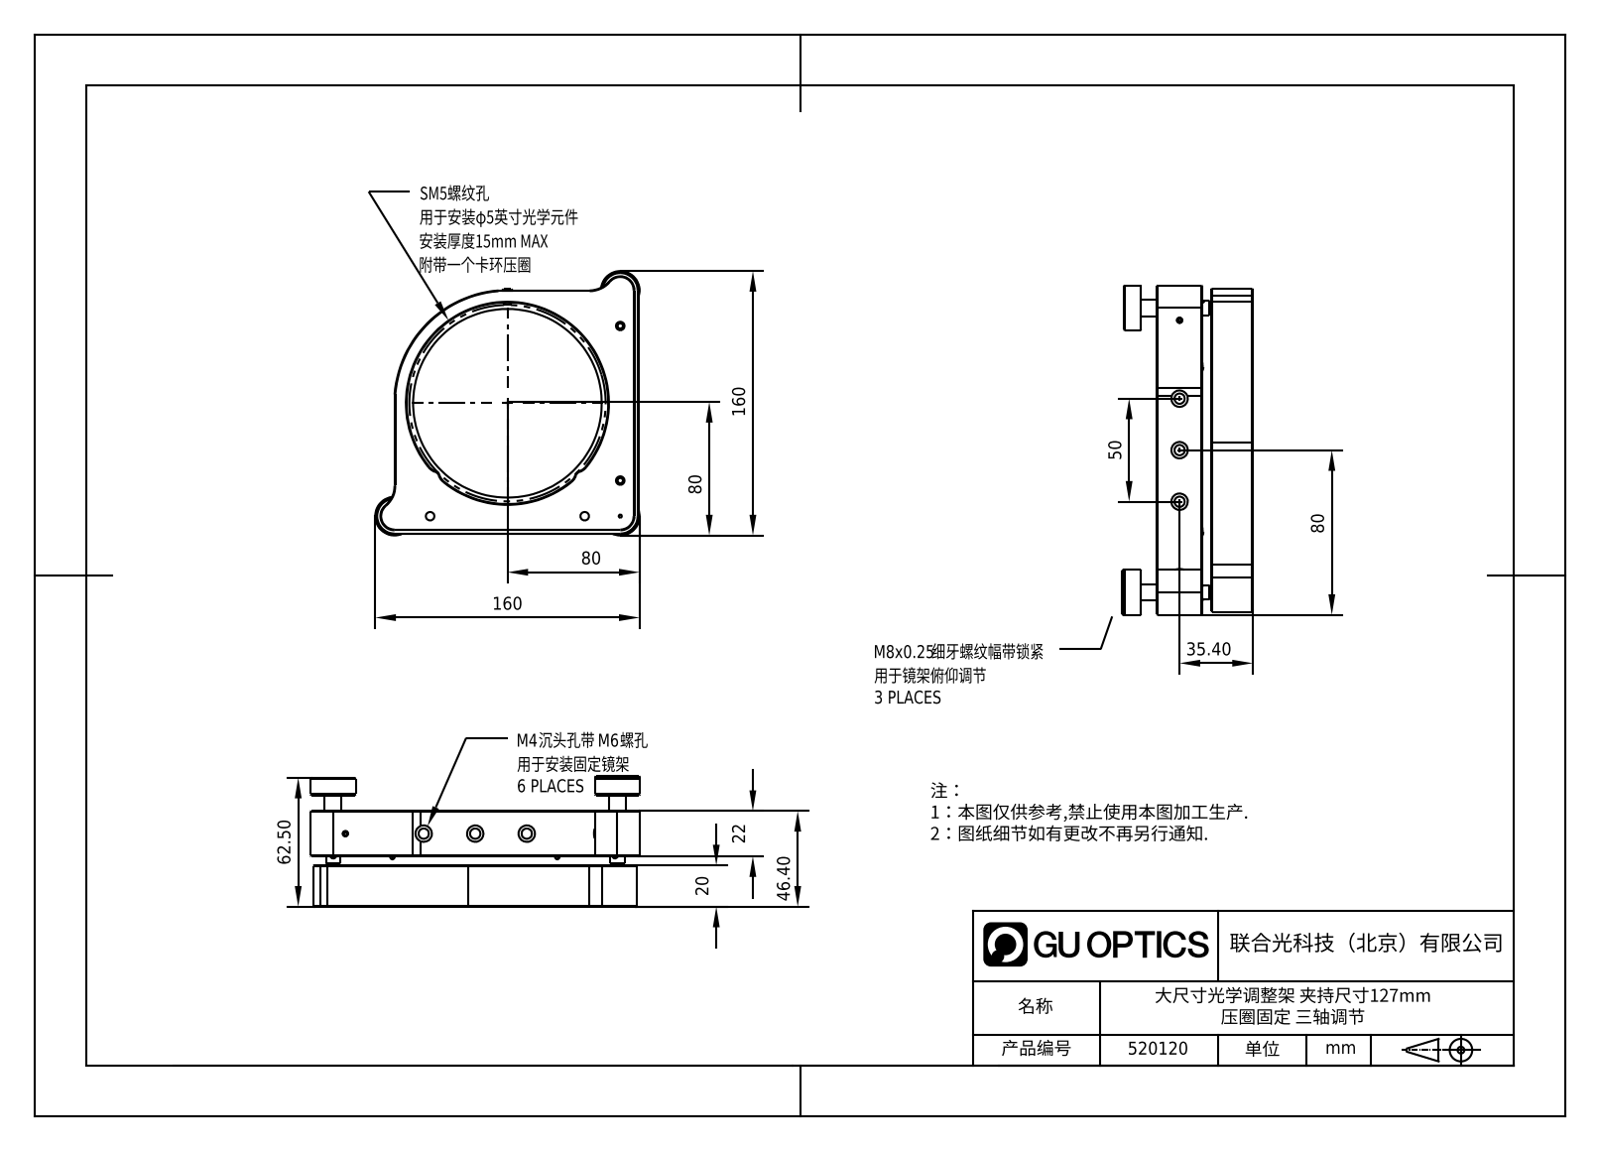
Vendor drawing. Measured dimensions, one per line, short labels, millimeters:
written by: SolidWorks 2021 (CONFIG_CONTROL_DESIGN)
unit: mm
bodies: 0 solids, 352 faces (107 planar, 142 cylindrical, 103 other)
size: 160 × 160 × 63.24
holes: 10× ⌀8, 6× ⌀5, 4× ⌀3.3, 3× ⌀3, 3× ⌀6, 3× ⌀12, 2× ⌀1.5, 2× ⌀2.5, 1× ⌀13.5, 1× ⌀122, 1× ⌀123, 1× ⌀127
bosses: 4× ⌀2, 3× ⌀22, 3× ⌀8, 3× ⌀7, 2× ⌀13
rounds: 8× R1.05, 4× R6, 3× R9.5, 2× R8, 2× R10, 1× R64.5, 1× R72
face distances: 20, 22, 4.4, 24.4, 26.4, 46.4, 1.5, 150.41, 151.91, 20.5
hole spacings: 25, 97.58, 28, 30, 38, 50, 63, 79.26
